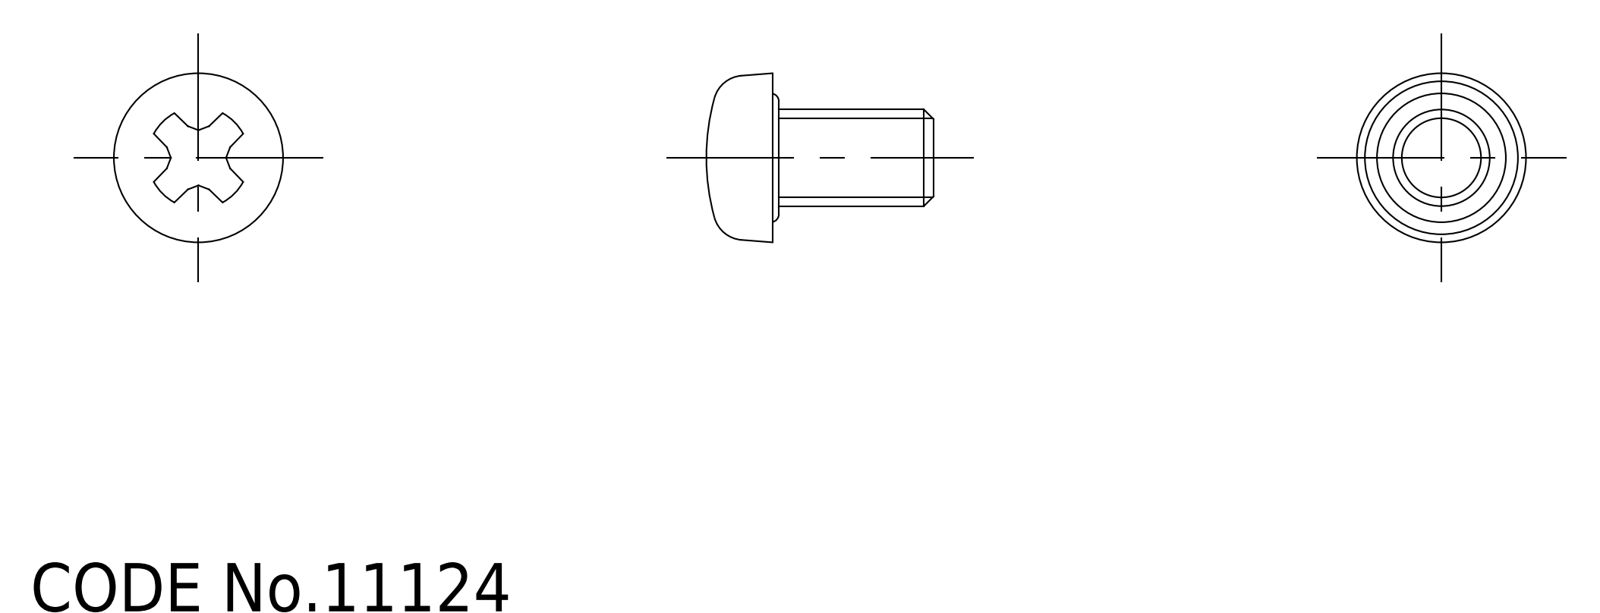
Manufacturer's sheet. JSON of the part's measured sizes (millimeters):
{"part_name": "TL_416_M6_10; screw", "step_written_by": "SolidWorks 2015 (AUTOMOTIVE_DESIGN)", "units": "millimeters", "bodies": {"solids": 2, "faces": 40, "planar": 20, "cylindrical": 8, "other": 12}, "overall_size": [13.99, 10.5, 10.5], "volume_mm3": 544, "surface_area_mm2": 556, "round_holes": [[9.5, 1]], "round_bosses_or_shafts": [[6, 1]], "partial_cylinders_radius": [[3.15, 1]], "face_to_face_distances": [2.5, 13.1, 10.6, 3.1, 0.6, 10, 1.8, 3.2]}
